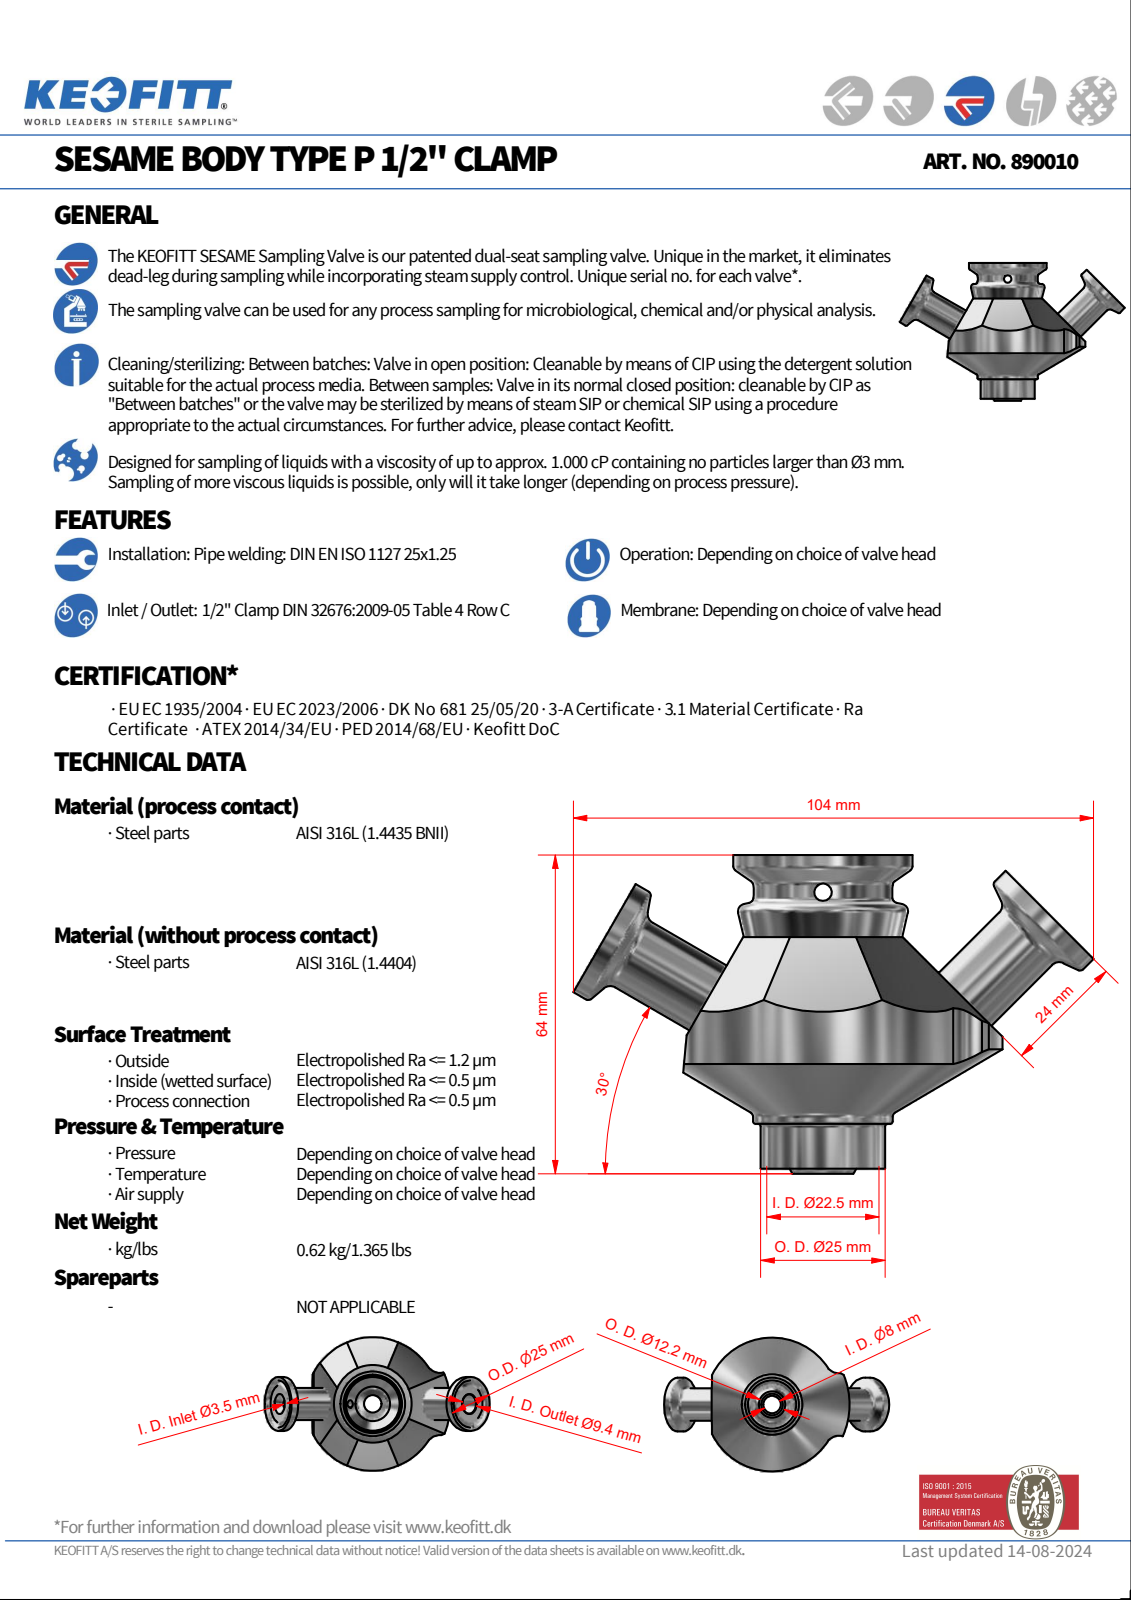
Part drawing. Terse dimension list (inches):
name: 890010
written by: Autodesk Inventor 2020 (AUTOMOTIVE_DESIGN)
unit: in
bodies: 1 solid, 104 faces (27 planar, 36 cylindrical, 41 other)
size: 4.11 × 2.52 × 2.441
volume: 4.922 in³; area: 34.85 in²
holes: 3× ⌀0.138, 2× ⌀0.858, 1× ⌀0.315, 1× ⌀0.354, 1× ⌀0.63, 1× ⌀0.886, 1× ⌀0.984, 1× ⌀1.024, 1× ⌀1.142, 1× ⌀1.181
bosses: 2× ⌀0.984, 2× ⌀0.591, 1× ⌀1.417, 1× ⌀1.13, 1× ⌀1.122, 1× ⌀1.102, 1× ⌀0.796
rounds: 2× R0.276, 1× R1.22, 1× R1.417
face distances: 1.652, 0.031, 0.775, 2.427, 0.914, 0.913, 2.309, 1.533, 0.118, 1.541
